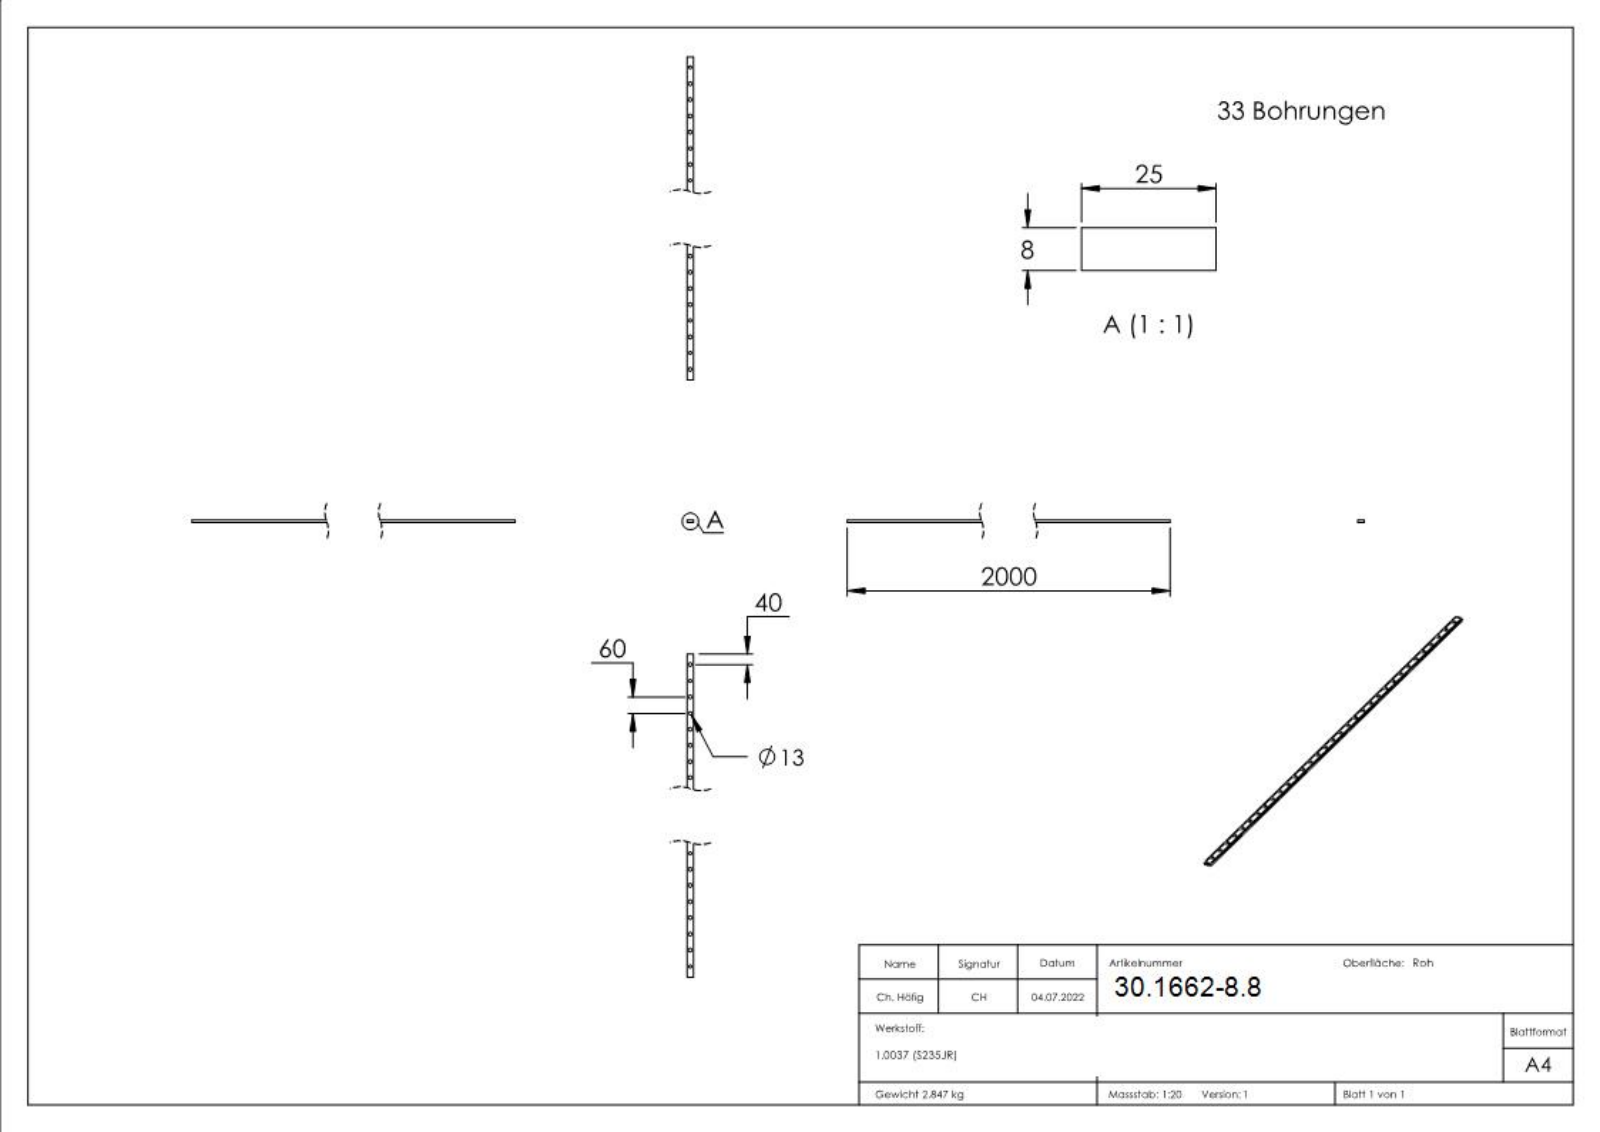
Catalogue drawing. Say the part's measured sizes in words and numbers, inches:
The part is named "1668-8". Its 3-D file was written by "SolidWorks 2018 (CONFIG_CONTROL_DESIGN)". It is 1 solid with 275 faces: 122 planar, 33 cylindrical and 120 other. Overall it measures 78.74 by 0.984 by 0.315 inches. Its volume is 22.27 cubic inches and its surface area 208.4 square inches. Round holes: 33 of diameter 0.512. The main face-to-face distances are 0.315, 0.984, 78.74, 0.311, 0.045, 0.079, 0.129, 0.05, 0.013, 0.452. The hole center spacings are 2.362, 4.724, 7.087, 9.449, 11.811, 14.173, 16.535, 18.898.
